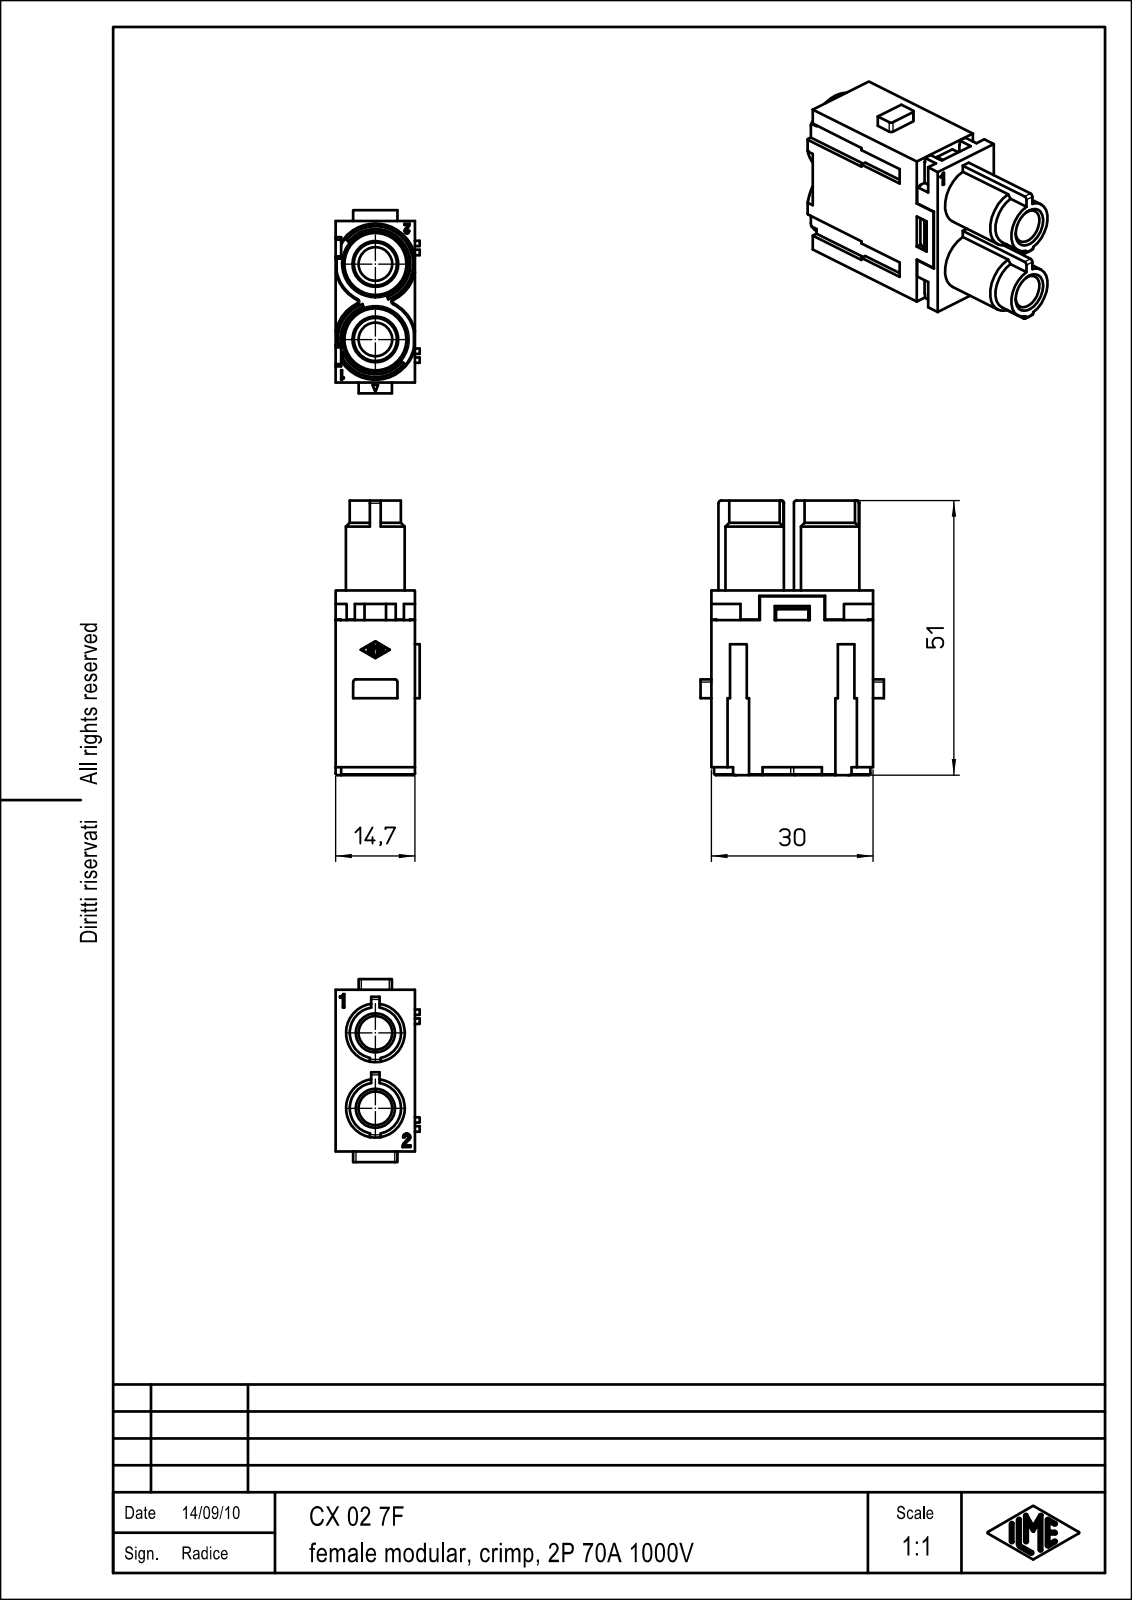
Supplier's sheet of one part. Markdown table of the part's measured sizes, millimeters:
| quantity | value |
| --- | --- |
| part name | CX_02_7F_internet |
| STEP written by | Creo Elements/Direct Modeling 17.0C 05-Feb-2011 (C) Parametric Technology GmbH (AUTOMOTIVE_DESIGN) |
| units | millimeters |
| bodies | 1 solid, 423 faces (321 planar, 59 cylindrical, 43 other) |
| overall size | 51 × 34 × 15.6 |
| volume | 10 777 mm³ |
| surface area | 8 689 mm² |
| round holes (diameter × count) | 6.25 × 2, 8 × 2, 8.5 × 2, 10 × 2, 11.5 × 2, 12 × 2 |
| round bosses / shafts (diameter × count) | 10.9 × 2, 9.52 × 2 |
| partial cylindrical surfaces (radius × count) | 0.5 × 6, 0.1 × 5, 0.3 × 4, 6.5 × 2, 7 × 2, 7.5 × 2 |
| main face-to-face distances | 14.7, 30, 1, 13.7, 1.5, 3, 1.1, 3.3, 1.8, 5.5 |
| hole center spacings | 14 |
